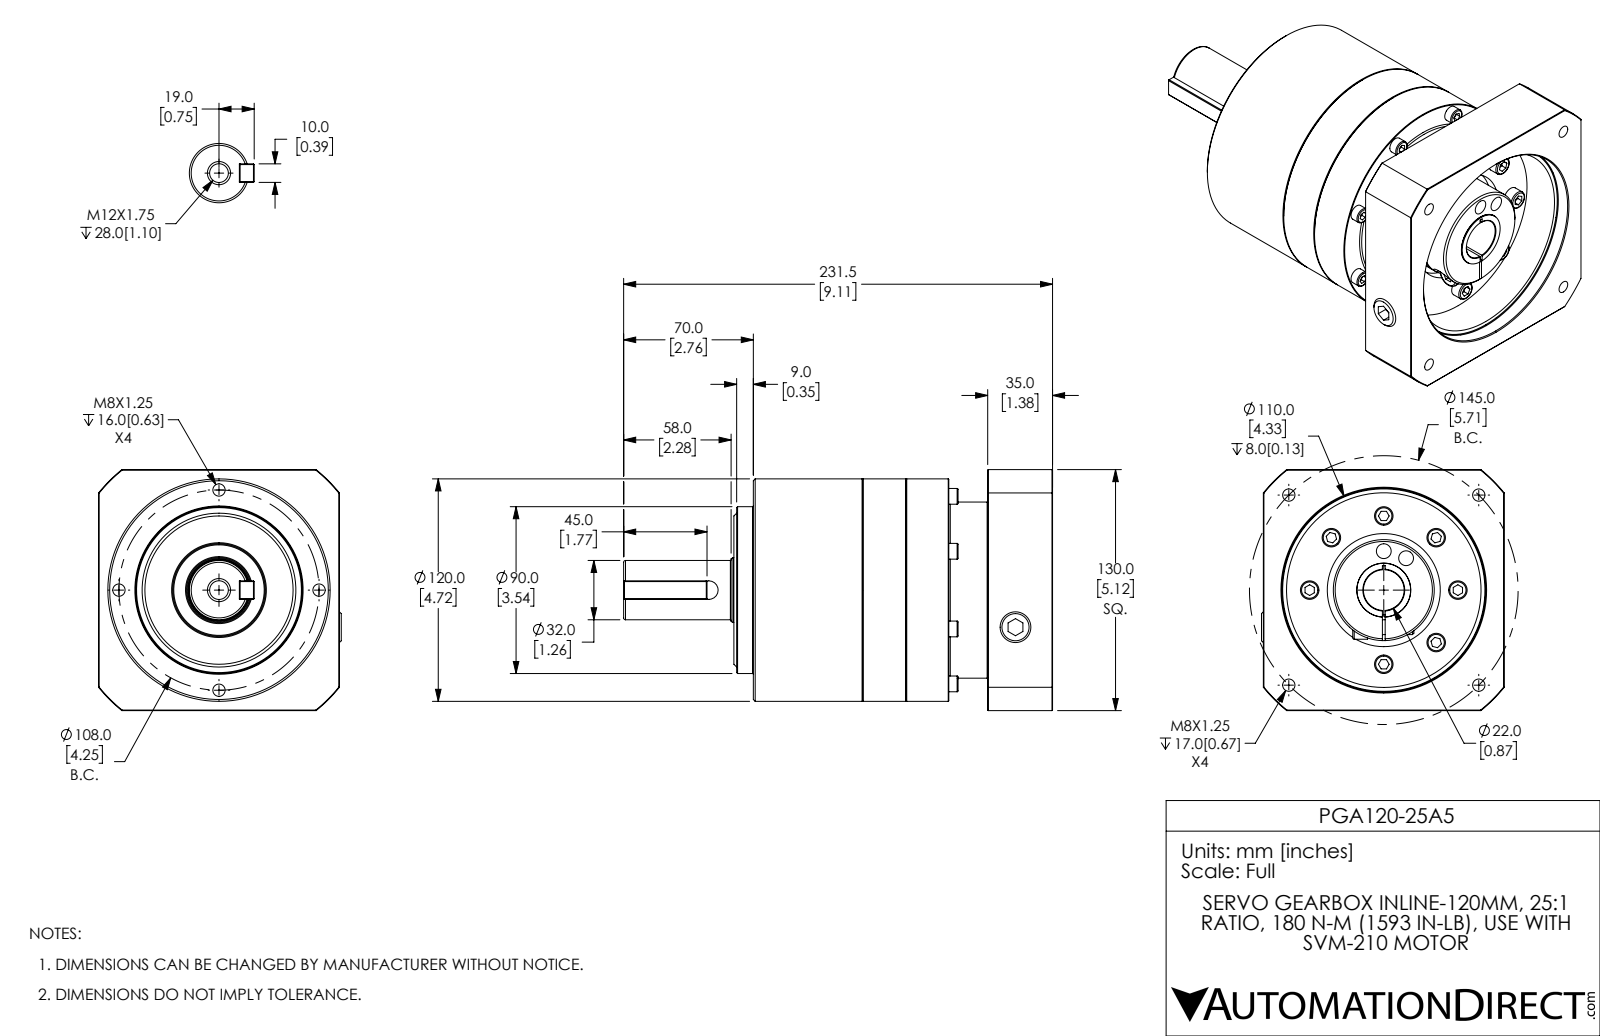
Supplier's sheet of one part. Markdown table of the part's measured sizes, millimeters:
| quantity | value |
| --- | --- |
| part name | PGA120-25A5 |
| STEP written by | SolidWorks 2019 (CONFIG_CONTROL_DESIGN) |
| units | millimeters |
| bodies | 1 solid, 448 faces (193 planar, 101 cylindrical, 154 other) |
| overall size | 231.5 × 131 × 130 |
| volume | 1 780 000 mm³ |
| surface area | 145 362 mm² |
| round holes (diameter × count) | 6.65 × 8, 8 × 2, 8.8 × 1, 10.11 × 1, 14.25 × 1, 22 × 1, 61 × 1, 105 × 1, 110 × 1 |
| round bosses / shafts (diameter × count) | 8.5 × 8, 10 × 7, 120 × 1, 95 × 1, 90 × 1, 54.5 × 1, 35 × 1, 32 × 1 |
| partial cylindrical surfaces (radius × count) | 3.32 × 1, 5 × 1, 7 × 1, 83.5 × 1 |
| main face-to-face distances | 130, 35, 6, 29, 161.5, 132.5, 126.5, 27, 21, 172 |
| hole center spacings | 51.34, 117.09, 54, 72.51, 76.37, 102.54, 21, 57.94 |
